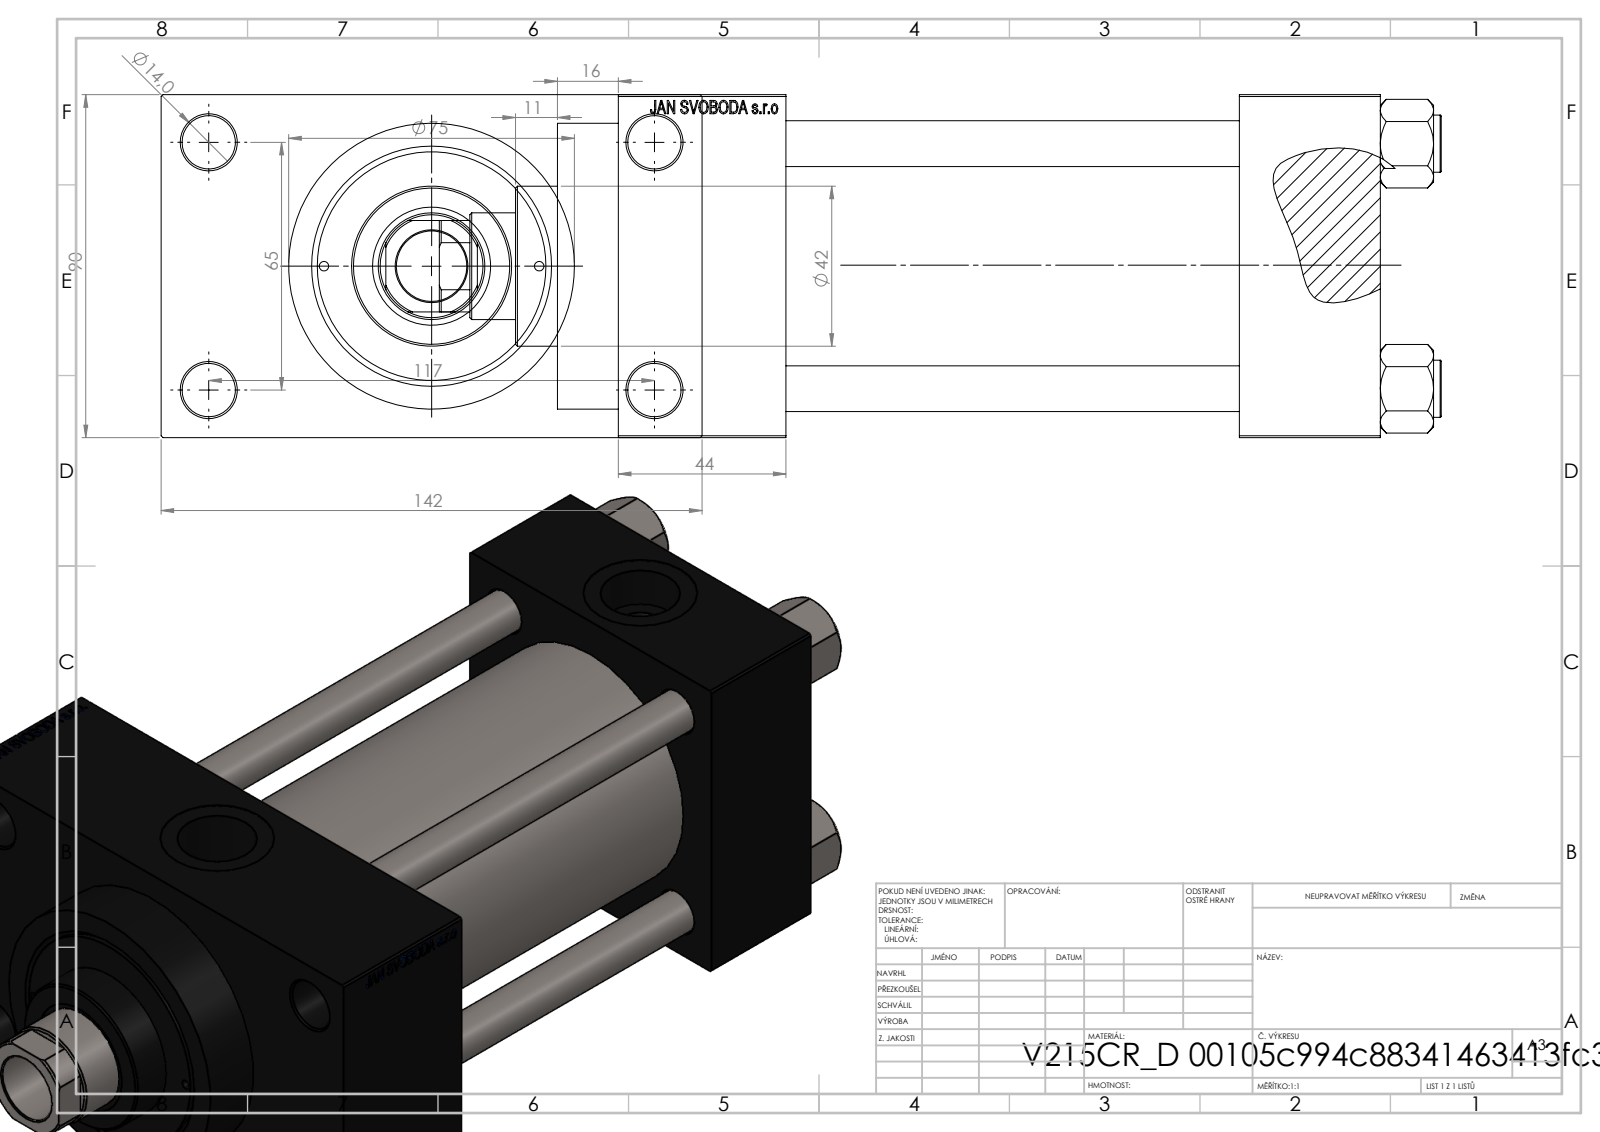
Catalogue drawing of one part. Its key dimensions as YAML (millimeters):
part_name: "NUT_M5_D; V215CR_D_Body; V215CR_VCP_D; V215_VC_A (+1 more)"
step_written_by: "SolidWorks 2019 (CONFIG_CONTROL_DESIGN)"
units: millimeters
bodies: {solids: 11, faces: 1112, planar: 499, cylindrical: 93, other: 520}
overall_size: [263, 142, 90]
volume: 1206000
surface_area: 237730
round_holes:
  - {diameter: 12, count: 4}
  - {diameter: 14, count: 4}
  - {diameter: 2.5, count: 2}
  - {diameter: 7, count: 2}
  - {diameter: 20.96, count: 2}
  - {diameter: 30, count: 2}
  - {diameter: 18.5, count: 1}
  - {diameter: 28, count: 1}
  - {diameter: 31, count: 1}
  - {diameter: 50, count: 1}
  - {diameter: 60, count: 1}
  - {diameter: 63, count: 1}
round_bosses_or_shafts:
  - {diameter: 15, count: 4}
  - {diameter: 75, count: 1}
  - {diameter: 69, count: 1}
  - {diameter: 42, count: 1}
partial_cylinders:
  - {radius: 13.5, count: 1}
face_to_face_distances: [90, 119, 37, 156, 163, 200, 44, 26, 116, 142]
hole_center_spacings: [26.35, 32.39, 44.4, 45.47, 64.3, 66.92, 68.42, 69.81]
